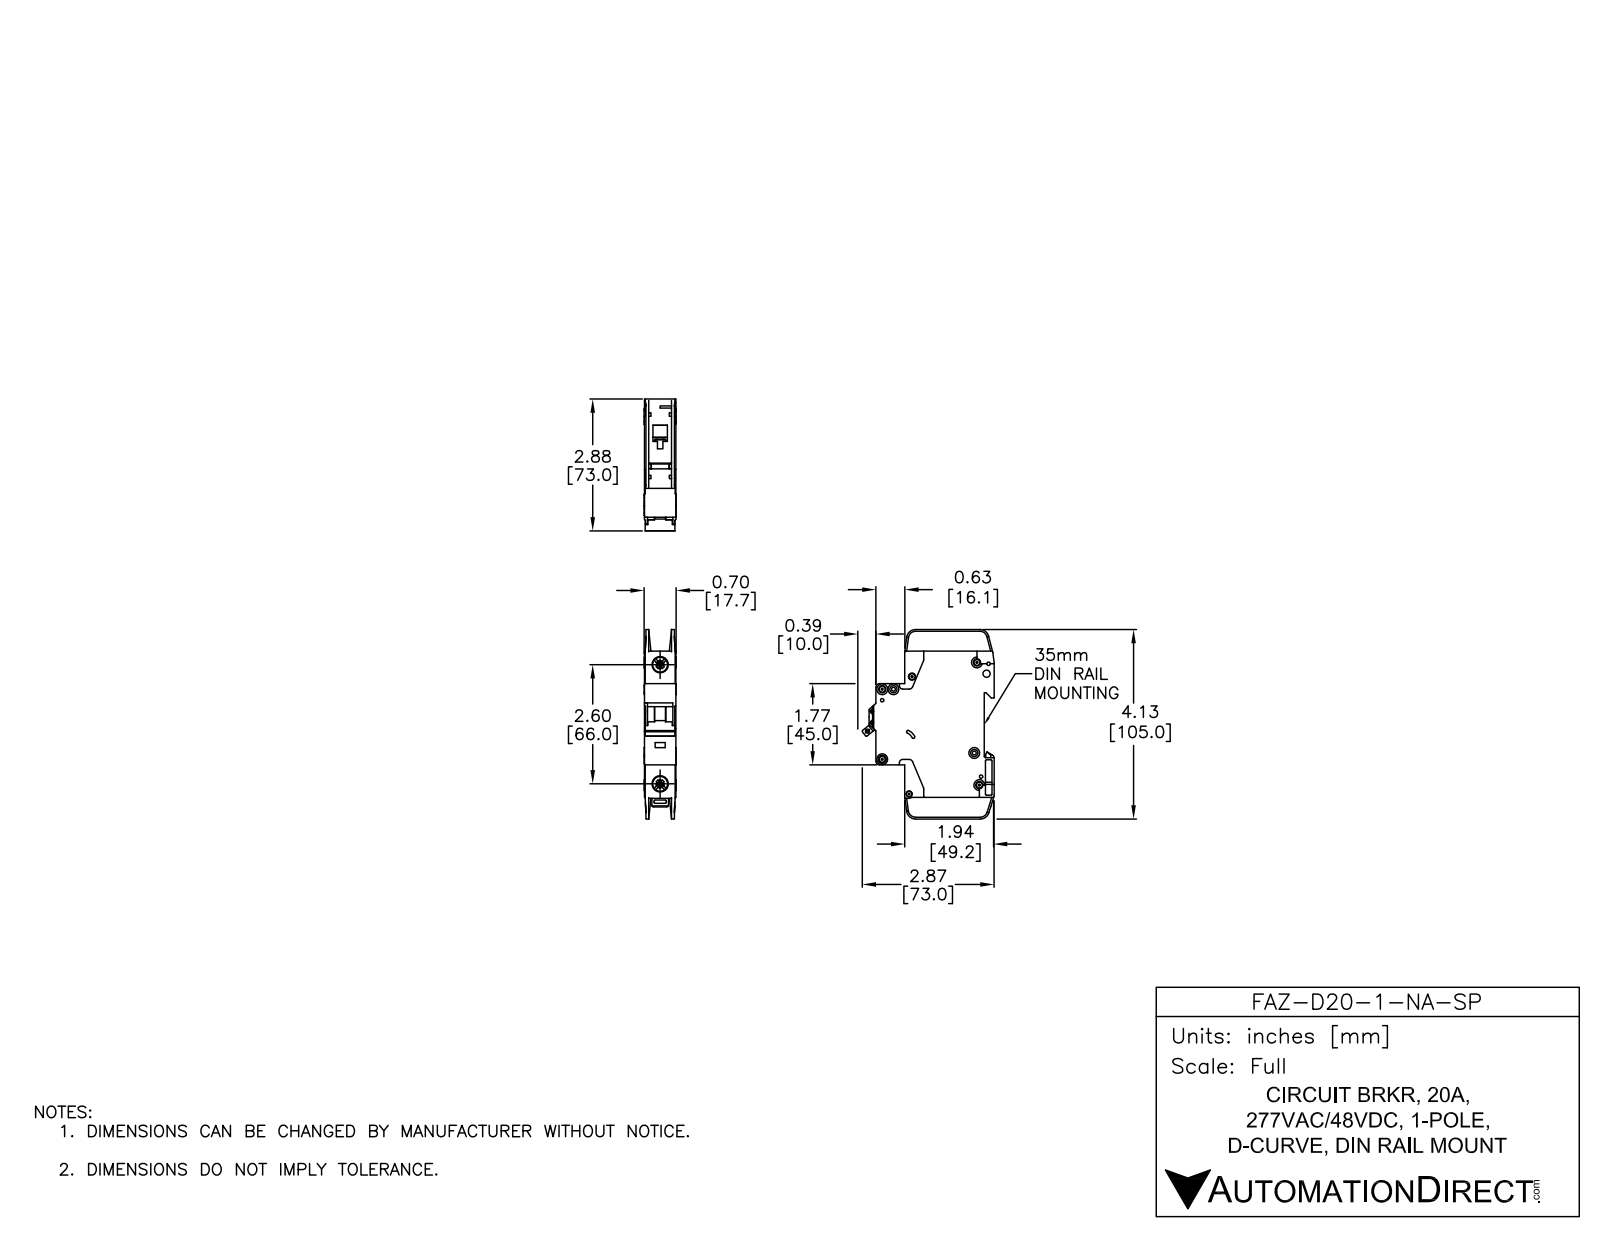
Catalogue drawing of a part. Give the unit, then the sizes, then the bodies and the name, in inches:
Units: inches
Overall size (bounding box): 4.134 × 2.876 × 0.697
Round holes (diameter × count): ⌀0.142 ×7, ⌀0.043 ×2, ⌀0.059 ×2, ⌀0.157 ×2, ⌀0.281 ×2, ⌀0.323 ×2, ⌀0.075 ×1, ⌀0.085 ×1, ⌀0.087 ×1, ⌀0.1 ×1, ⌀0.13 ×1, ⌀0.134 ×1
Round bosses / shafts (diameter × count): ⌀0.236 ×7, ⌀0.098 ×1
Partial cylindrical surfaces — rounded edges, fillets, slot ends (radius × count): R0.01 ×29, R0.02 ×18, R0.039 ×10, R0.079 ×10, R0.197 ×5, R0.157 ×4, R0.071 ×3, R0.008 ×2
Main face-to-face distances: 0.689, 0.593, 0.028, 0.096, 0.069, 0.62, 0.524, 0.551, 0.496, 0.079
Hole centre spacings: 0.244, 0.204, 0.24, 0.322, 0.337, 0.343, 0.437, 0.49
Volume: 4.741 in³ · Surface area: 38.35 in²
Bodies: 3 solids, 784 faces (409 planar, 263 cylindrical, 112 other)
Part name (STEP PRODUCT): FAZ-D20-1-NA-SP
STEP written by: SolidWorks 2014 (AUTOMOTIVE_DESIGN)
